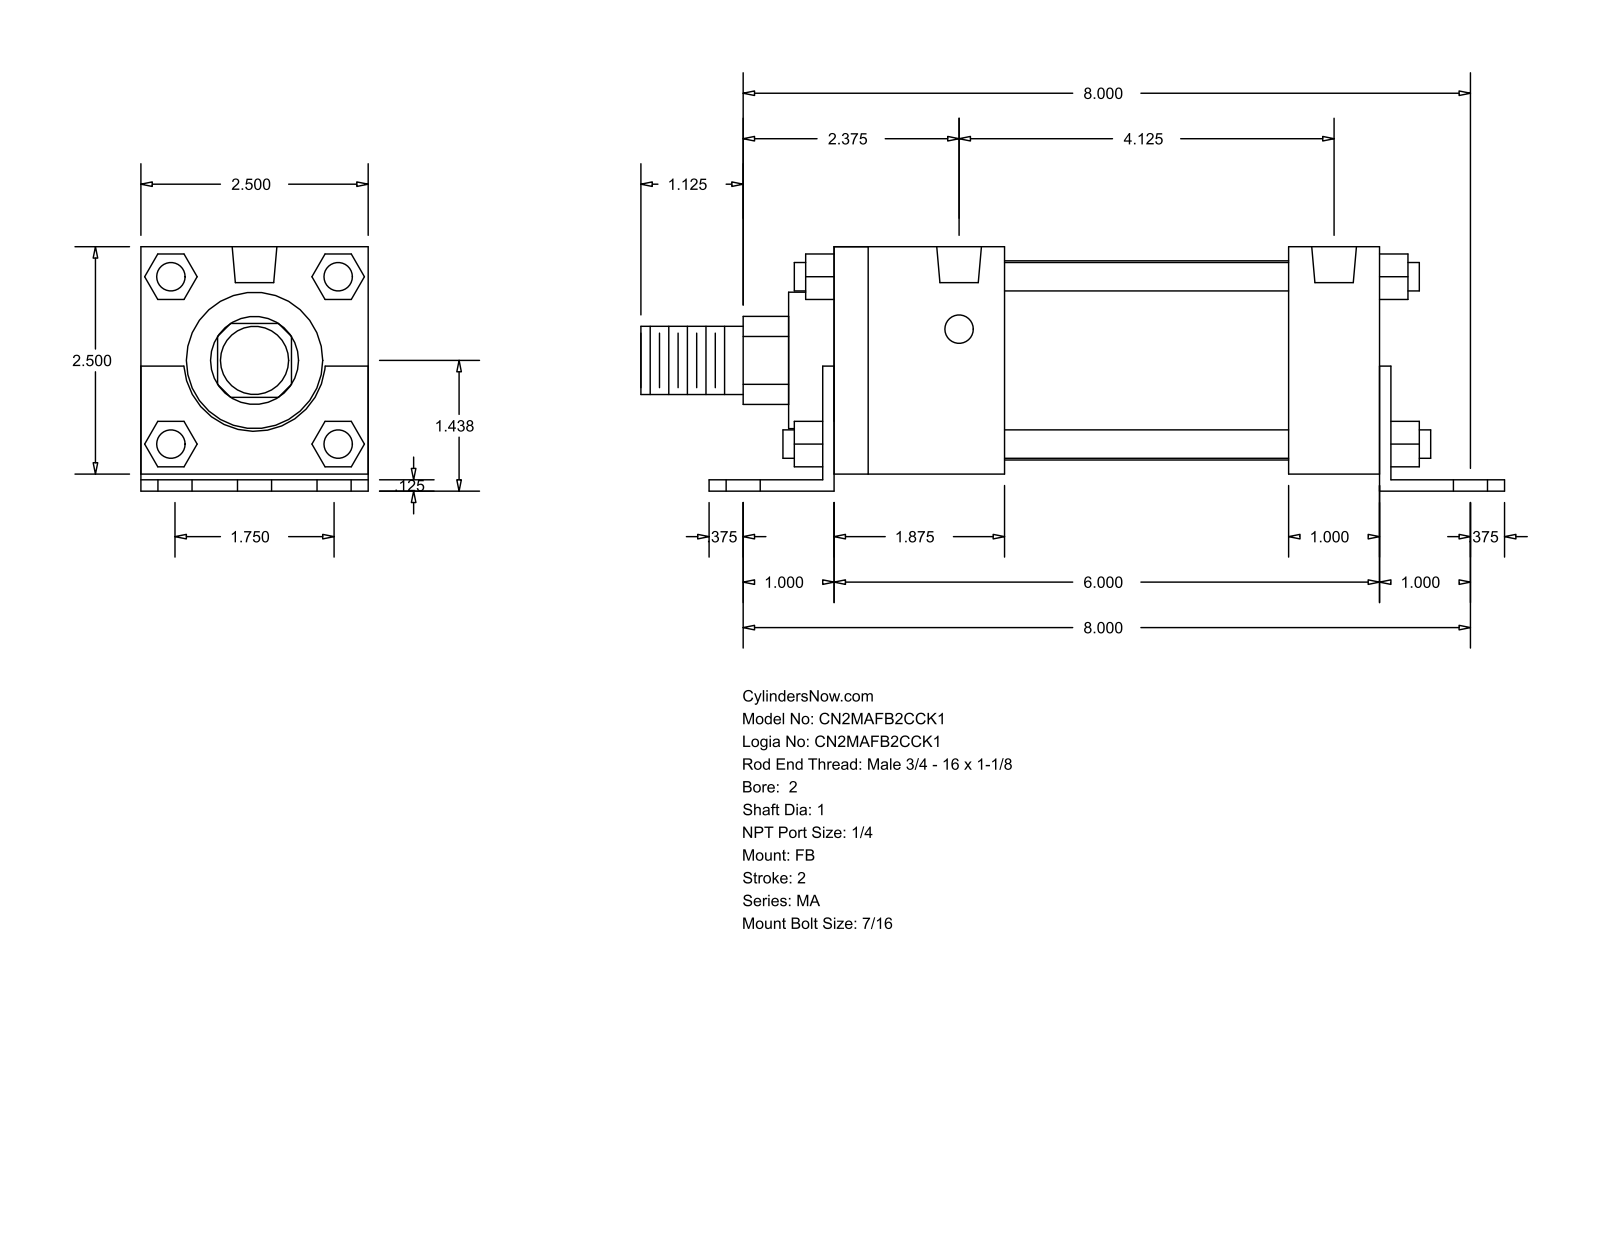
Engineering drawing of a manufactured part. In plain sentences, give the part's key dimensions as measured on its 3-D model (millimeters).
The part is named "MA_FB__0200_1". Its 3-D file was written by "GSSL Pune (CONFIG_CONTROL_DESIGN)". It is 0 solids with 140 faces: 105 planar, 35 cylindrical and 0 other. Overall it measures 241.3 by 68.26 by 63.5 millimeters. Round holes: 6 of diameter 11.11, 4 of diameter 7.94, 2 of diameter 12.49. Round bosses or shafts: 4 of diameter 7.94, 1 of diameter 55.63, 1 of diameter 38.1, 1 of diameter 25.4, 1 of diameter 19.05. Partial cylindrical surfaces (rounded edges, fillets, slot ends): 1 of radius 12.29, 1 of radius 19.81. The main face-to-face distances are 63.5, 3.17, 4.76, 68.26, 1.59, 65.09, 155.57, 12.7, 152.4, 28.57. The hole center spacings are 22.23, 204.41, 203.2, 44.11, 44.46, 64.3, 104.77, 144.59.
